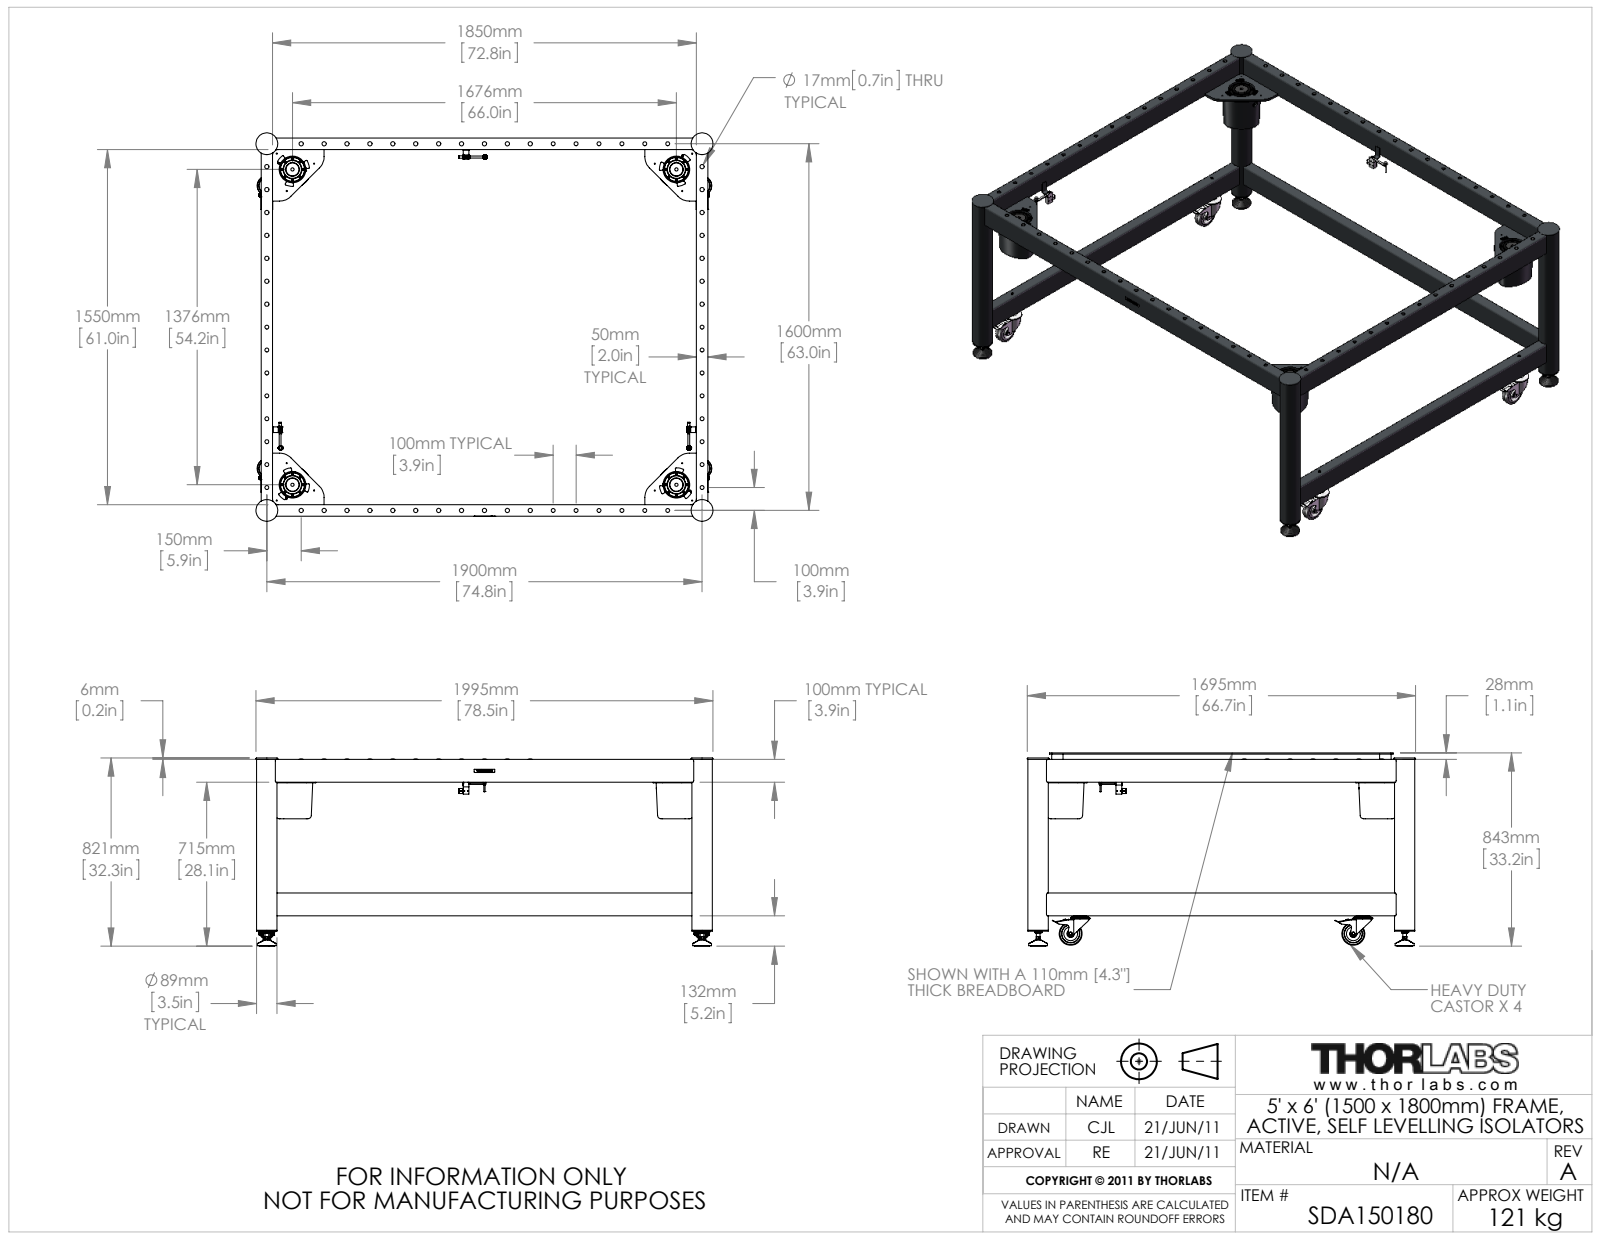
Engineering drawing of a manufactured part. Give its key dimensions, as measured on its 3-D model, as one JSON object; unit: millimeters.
{"part_name": "SDA150180", "step_written_by": "SolidWorks 2011 (CONFIG_CONTROL_DESIGN)", "units": "millimeters", "bodies": {"solids": 164, "faces": 6664, "planar": 2600, "cylindrical": 1879, "other": 2185}, "overall_size": [1995, 1695, 821], "volume_mm3": 18410000, "surface_area_mm2": 10040000, "round_holes": [[17, 68], [4.5, 36], [13, 36], [10, 28], [6.5, 18], [5, 15], [2.5, 14], [4.2, 13], [3.3, 8], [14, 8], [11, 7], [3.4, 6]], "round_bosses_or_shafts": [[16, 36], [7, 26], [4, 20], [5, 15], [8.5, 9], [8, 9], [82, 8], [64, 8]], "partial_cylinders_radius": [[3, 48], [4, 36], [7, 28], [2.75, 12], [7.5, 12], [124.09, 12], [0.5, 8], [5, 8]], "face_to_face_distances": [3, 47, 1900, 50, 44, 97, 583, 1600, 1903, 1853], "hole_center_spacings": [100, 200, 1902.63, 300, 1910.5, 1923.54, 400, 1941.65]}
